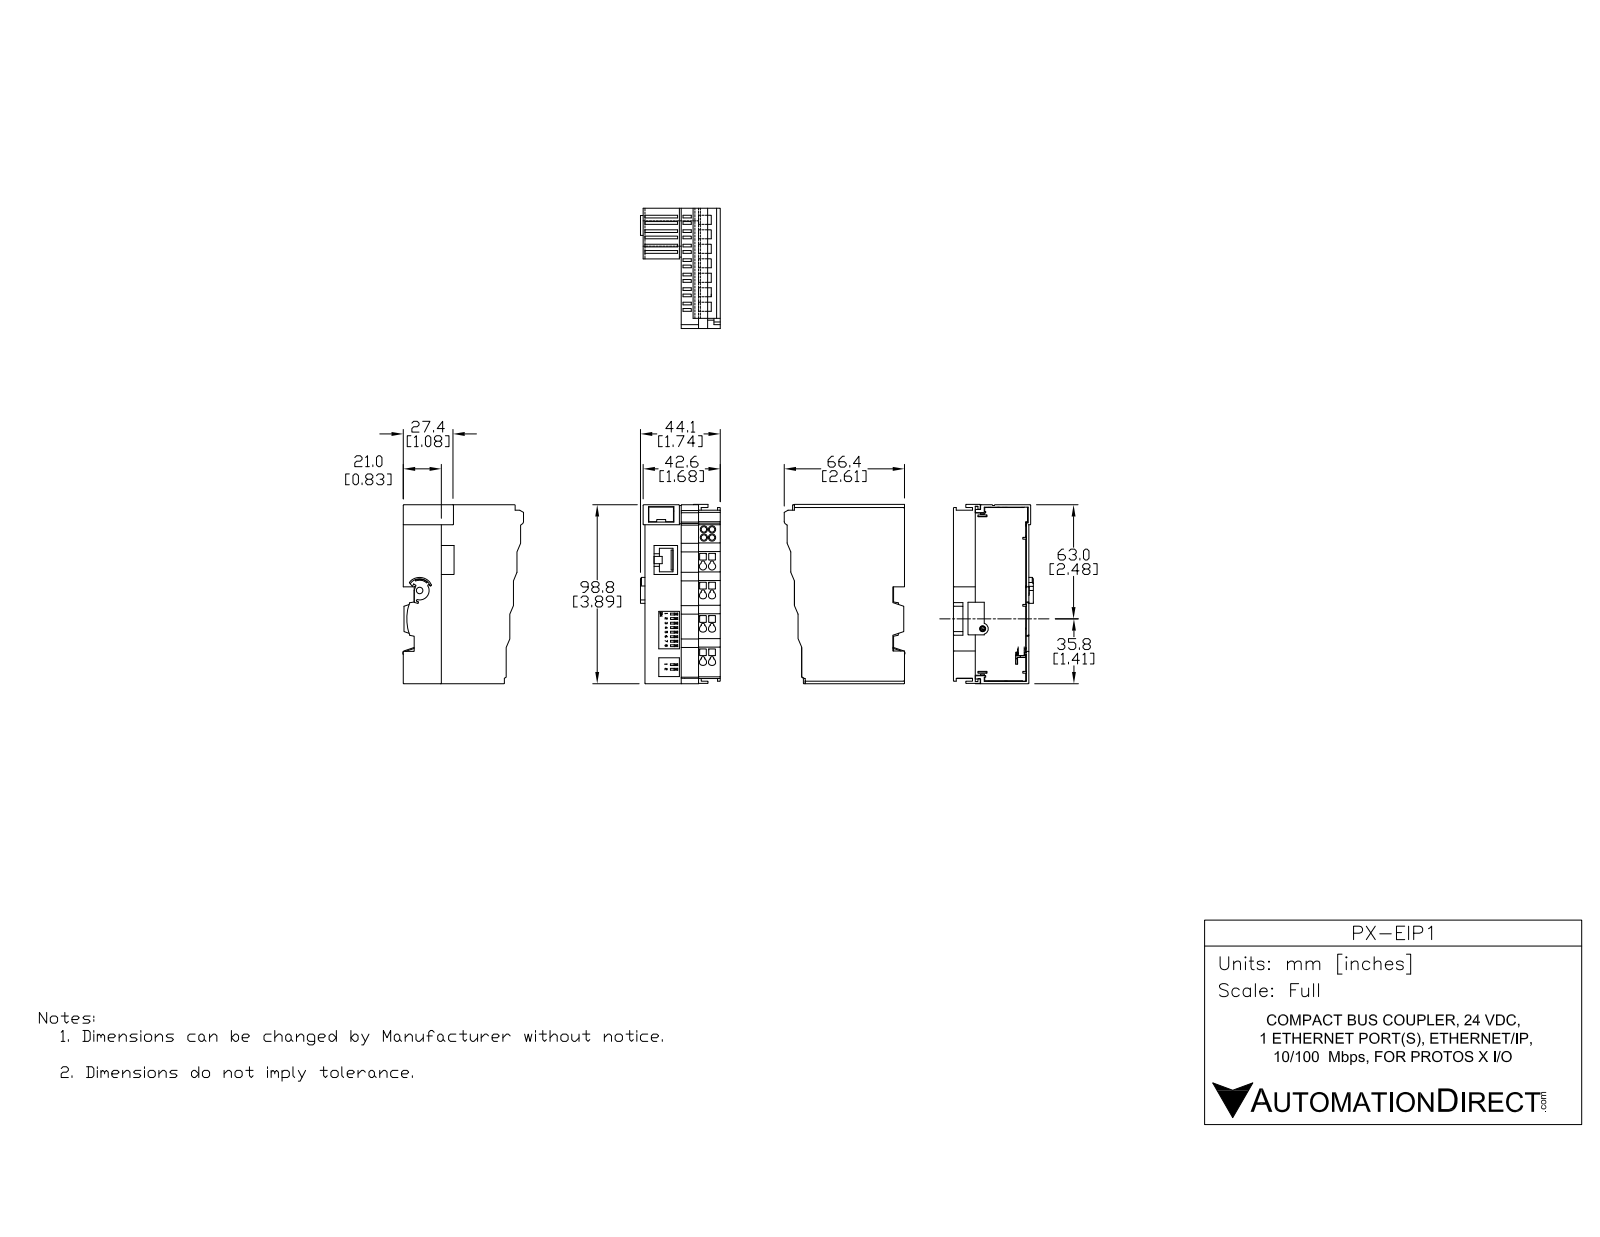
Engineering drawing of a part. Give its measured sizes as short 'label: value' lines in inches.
name: PX-EIP1
written by: SolidWorks 2016 (AUTOMOTIVE_DESIGN)
unit: in
bodies: 45 solids, 2099 faces (1570 planar, 421 cylindrical, 108 other)
size: 3.947 × 2.729 × 1.742
volume: 4.854 in³; area: 113.4 in²
holes: 8× ⌀0.157, 2× ⌀0.148
rounds: 77× R0.01, 47× R0.012, 20× R0.039, 18× R0.016, 12× R0.015, 12× R0.079, 4× R0.007, 4× R0.02
face distances: 0.039, 0.315, 0.512, 0.787, 0.472, 0.827, 0.354, 0.276, 1.102, 1.142
hole spacings: 0.197, 0.724, 0.751, 0.63, 0.66, 1.354, 1.369, 1.449
